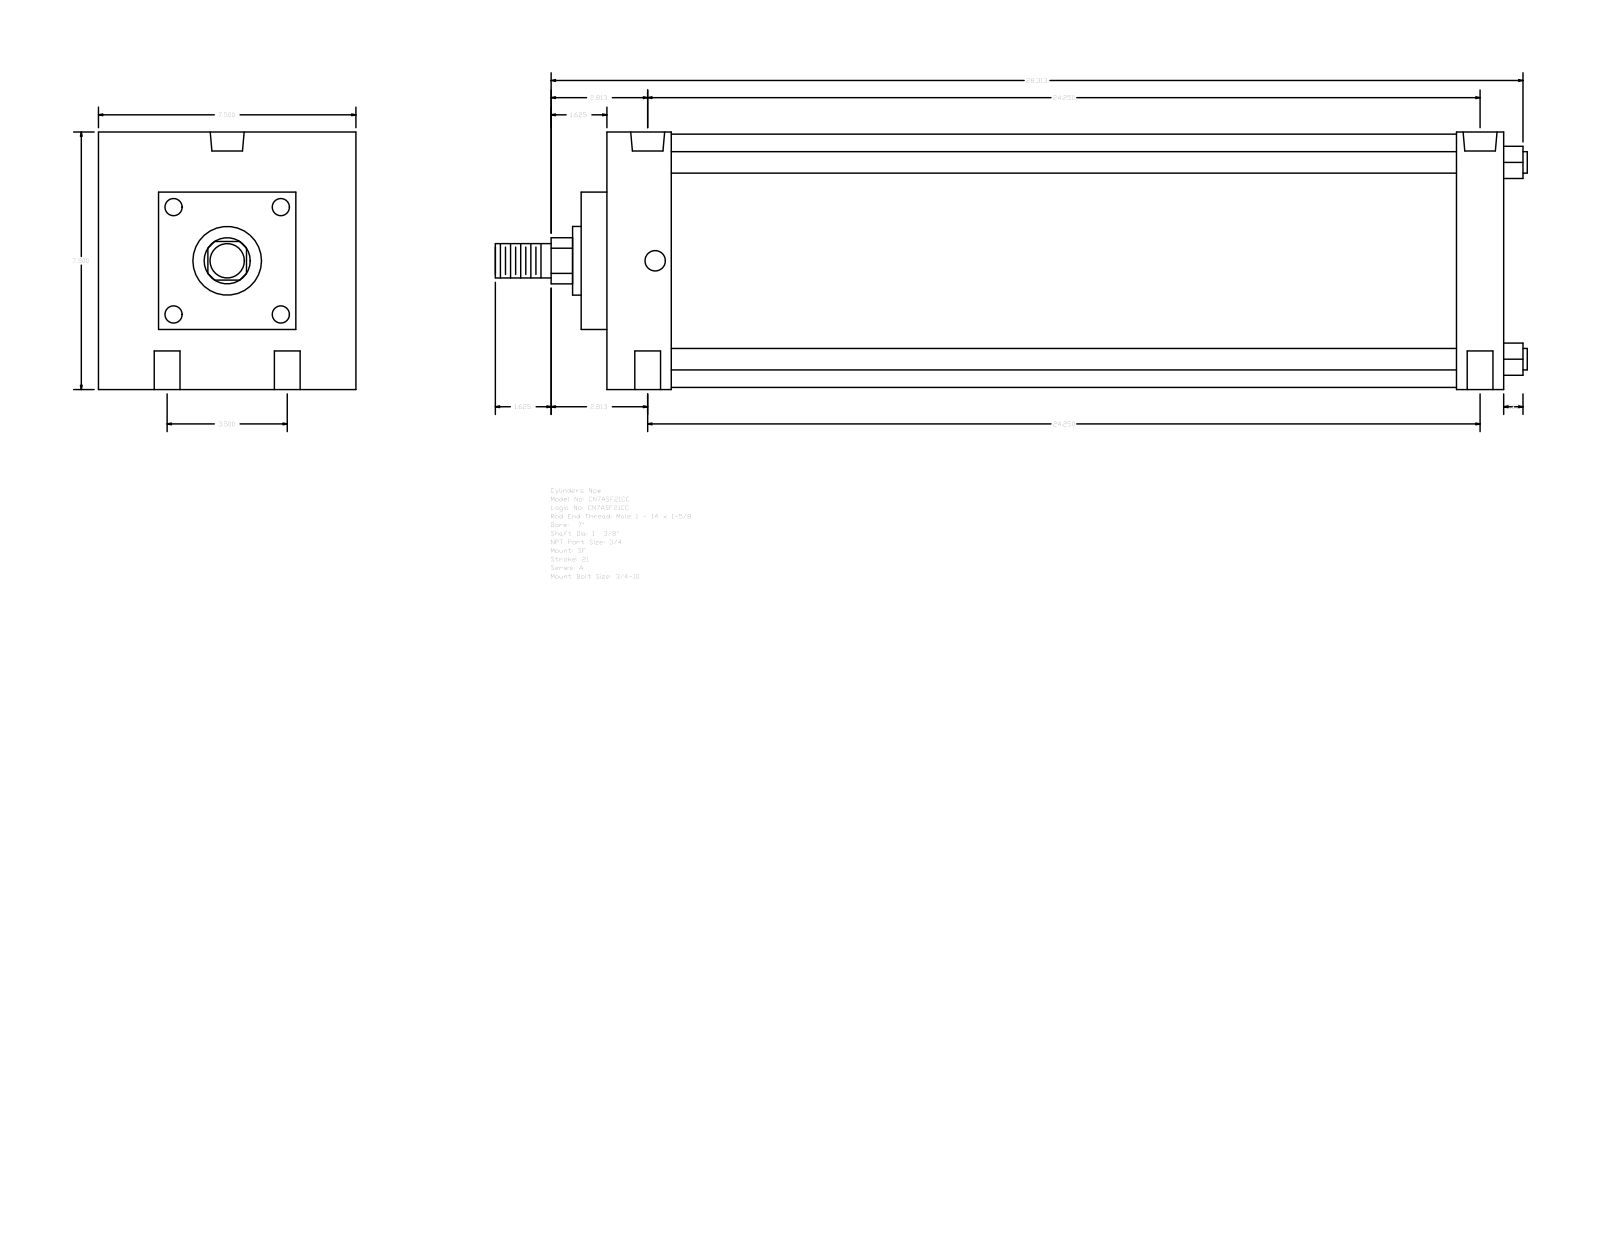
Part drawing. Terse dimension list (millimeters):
name: A_SF__0700_1.375
written by: GSSL Pune (CONFIG_CONTROL_DESIGN)
unit: mm
bodies: 0 solids, 93 faces (67 planar, 26 cylindrical, 0 other)
size: 763.59 × 190.5 × 190.5
holes: 4× ⌀19.05, 2× ⌀15.08, 2× ⌀25.12
bosses: 4× ⌀15.88, 1× ⌀187.32, 1× ⌀50.8, 1× ⌀34.92, 1× ⌀25.4
rounds: 1× R17.06
face distances: 190.5, 663.58, 19.04, 682.62, 66.67, 647.69, 47.63, 628.65, 581.02, 615.95
hole spacings: 44.45, 617.55, 615.95, 88.9, 622.33, 604.83
